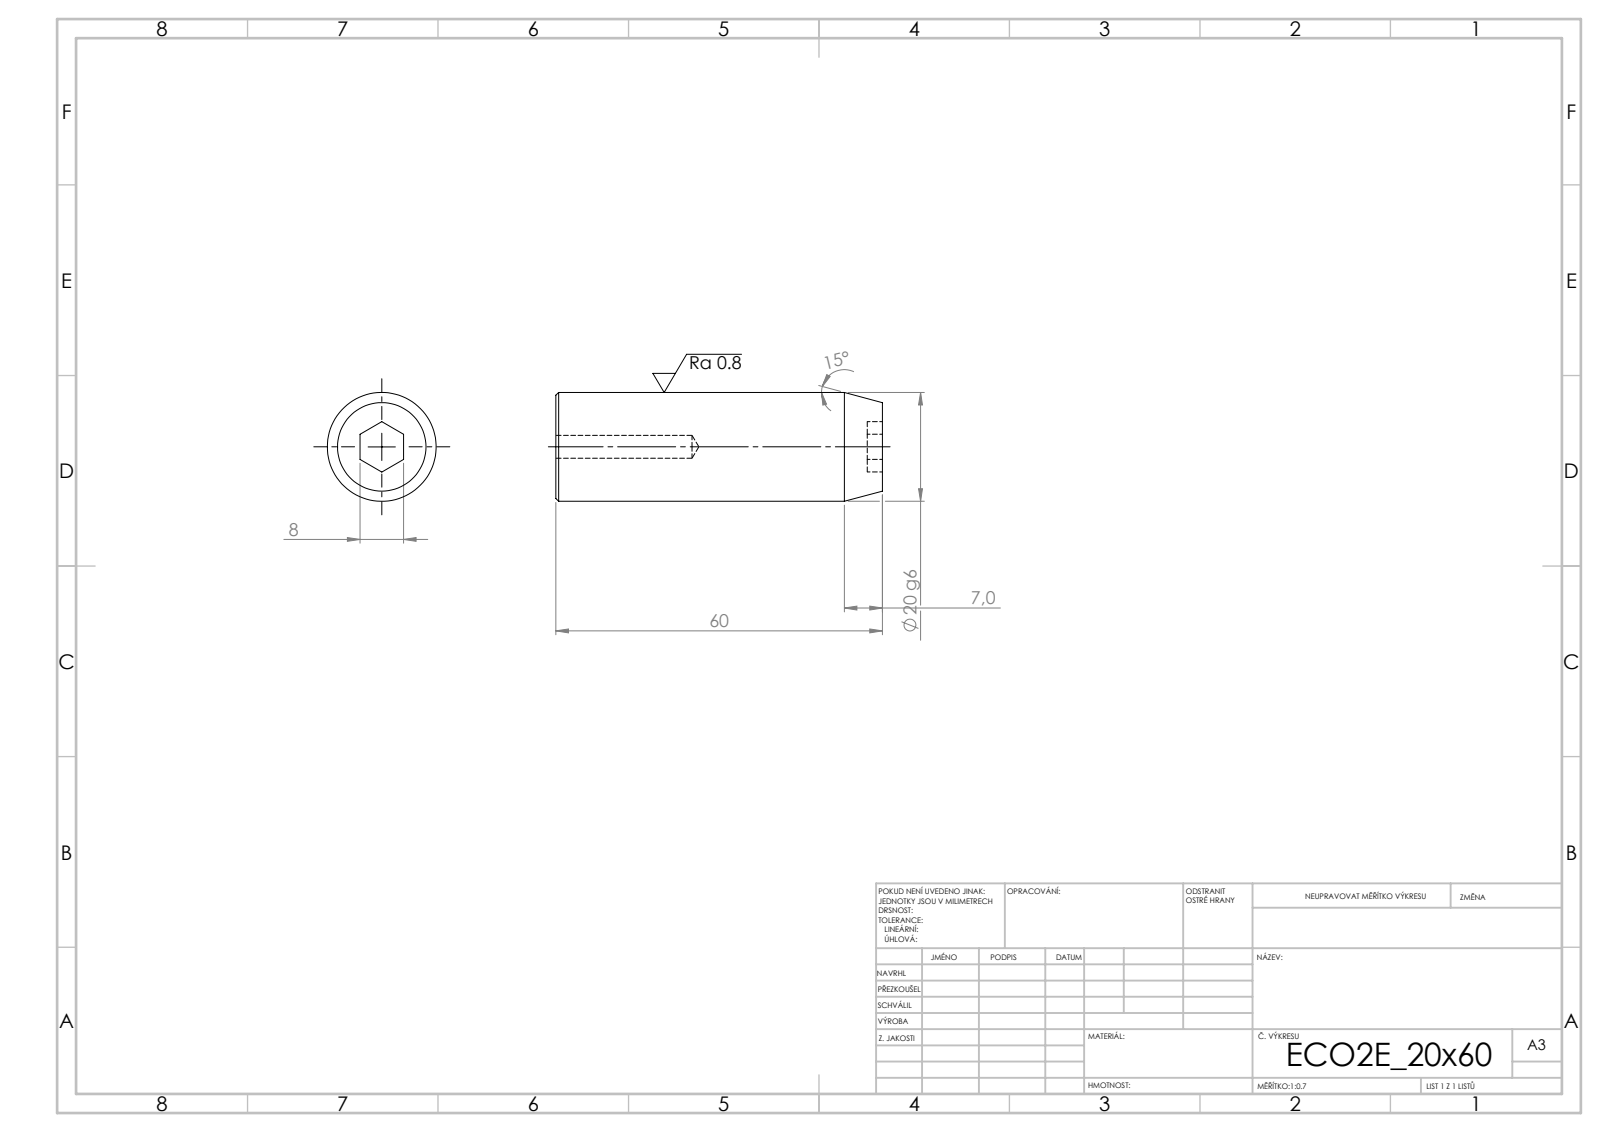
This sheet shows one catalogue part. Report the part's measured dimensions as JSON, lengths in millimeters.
{"step_written_by": "SolidWorks 2019 (CONFIG_CONTROL_DESIGN)", "units": "millimeters", "bodies": {"solids": 1, "faces": 19, "planar": 9, "cylindrical": 4, "other": 6}, "overall_size": [60, 20, 20], "volume_mm3": 17948, "surface_area_mm2": 4655, "round_holes": [[4.2, 1]], "round_bosses_or_shafts": [[20, 1]], "face_to_face_distances": [60, 2.8, 57.2, 8]}
